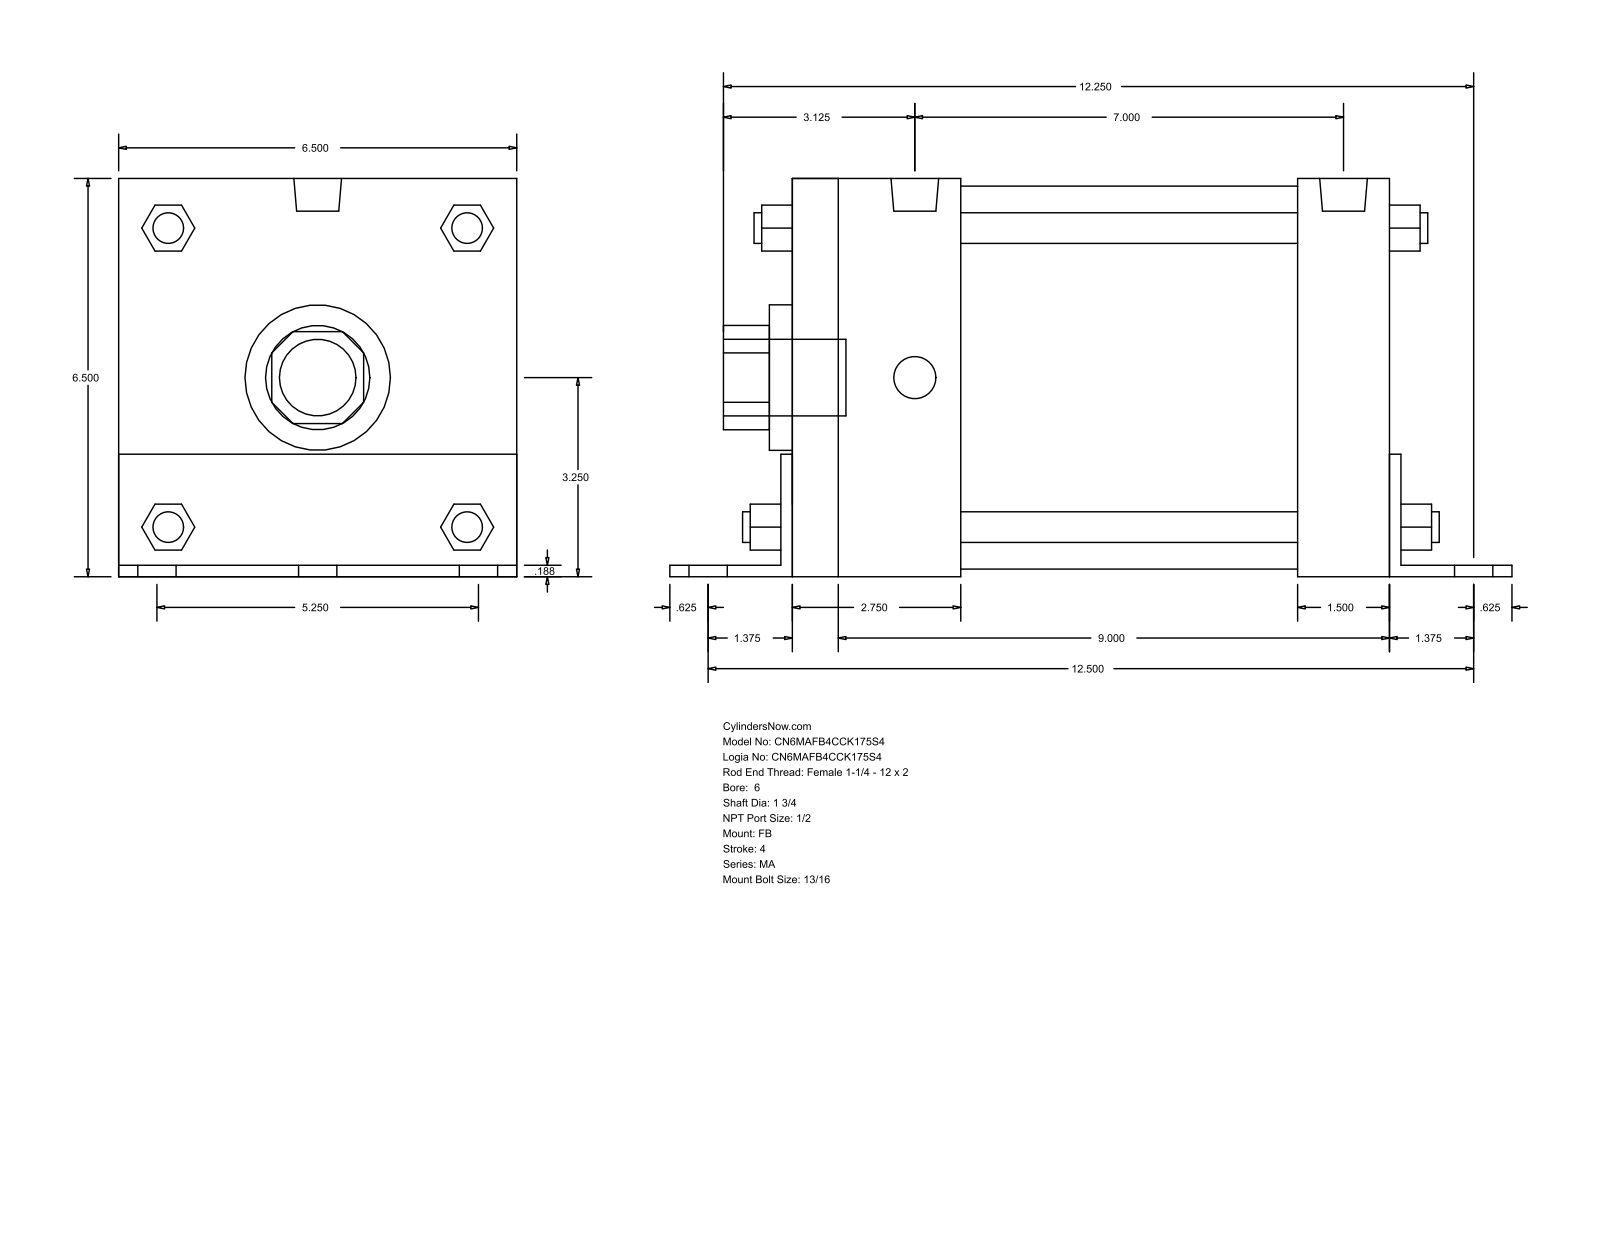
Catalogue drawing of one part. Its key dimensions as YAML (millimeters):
part_name: "MA_FB__0600_1.75"
step_written_by: "GSSL Pune (CONFIG_CONTROL_DESIGN)"
units: millimeters
bodies: {solids: 0, faces: 140, planar: 105, cylindrical: 35, other: 0}
overall_size: [349.25, 165.15, 165.1]
round_holes:
  - {diameter: 44.45, count: 1}
  - {diameter: 60.33, count: 1}
  - {diameter: 158.75, count: 1}
round_bosses_or_shafts:
  - {diameter: 20.64, count: 6}
  - {diameter: 17.46, count: 4}
  - {diameter: 12.7, count: 4}
  - {diameter: 19.77, count: 2}
  - {diameter: 31.75, count: 1}
partial_cylinders:
  - {radius: 21.63, count: 1}
  - {radius: 32.05, count: 1}
face_to_face_distances: [165.1, 4.76, 247.66, 165.15, 252.42, 4.71, 160.39, 257.18, 38.11, 74.61]
